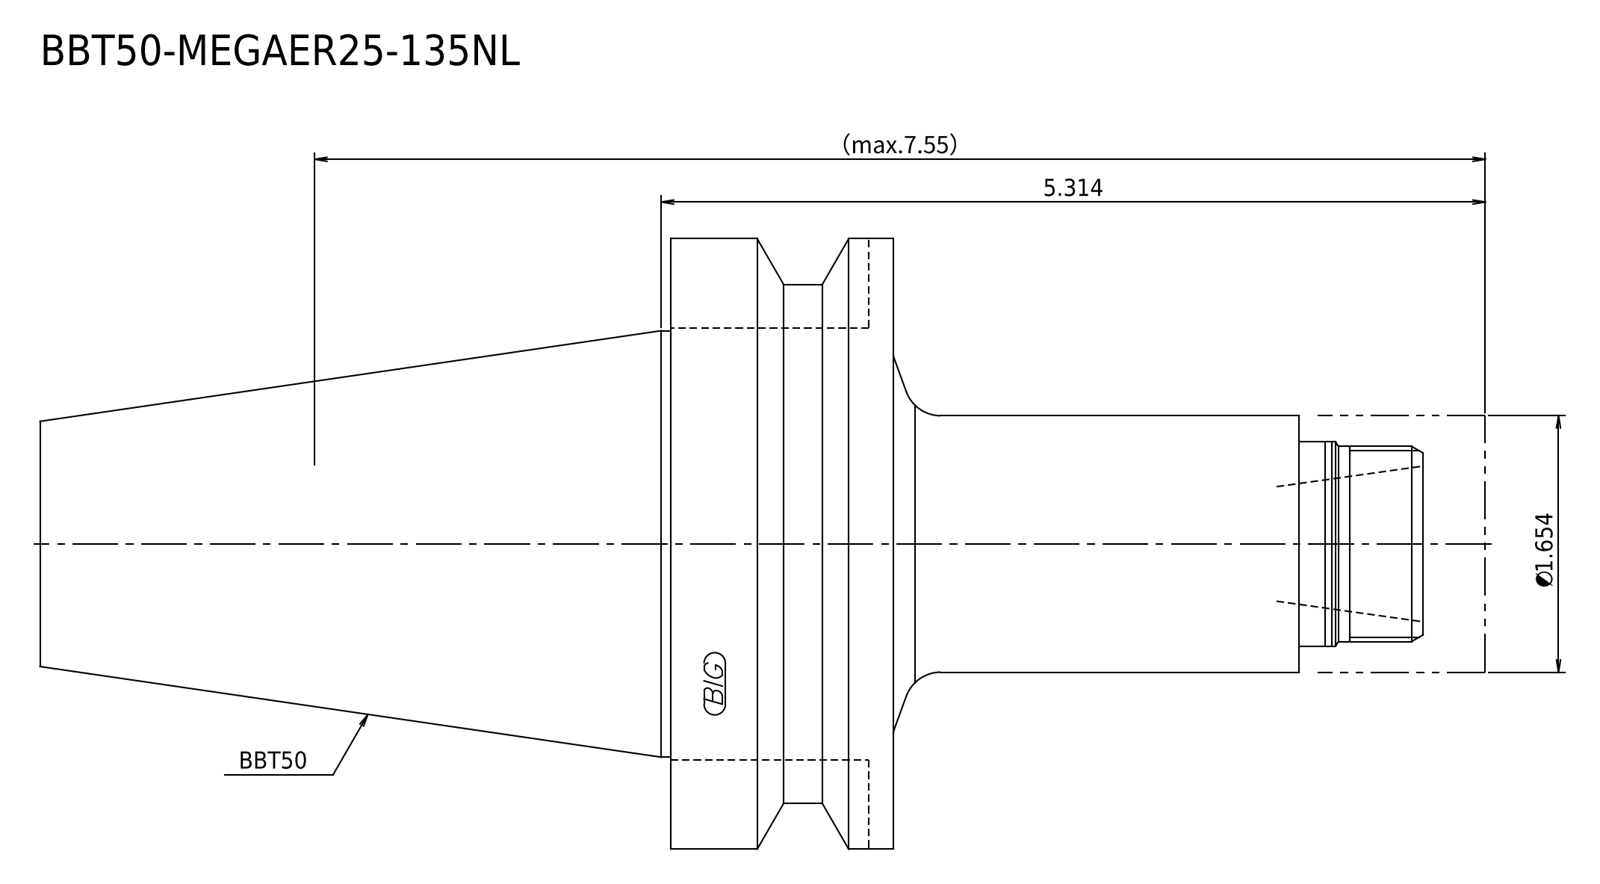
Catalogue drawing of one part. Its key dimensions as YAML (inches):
step_written_by: "Kubotek KeyCreator 2011 V10.0.2 (22737) (automotive_design)"
units: inches
bodies: {solids: 2, faces: 21, planar: 7, cylindrical: 8, other: 6}
overall_size: [236.8, 100, 100]
volume: 669643
surface_area: 61262
round_bosses_or_shafts:
  - {diameter: 100, count: 1}
  - {diameter: 85, count: 1}
  - {diameter: 69.85, count: 1}
  - {diameter: 42, count: 1}
  - {diameter: 33.5, count: 1}
  - {diameter: 32, count: 1}
face_to_face_distances: [36.5, 27.5, 97, 133.5, 69.5, 106, 236.8, 209.3, 139.8, 103.3]
